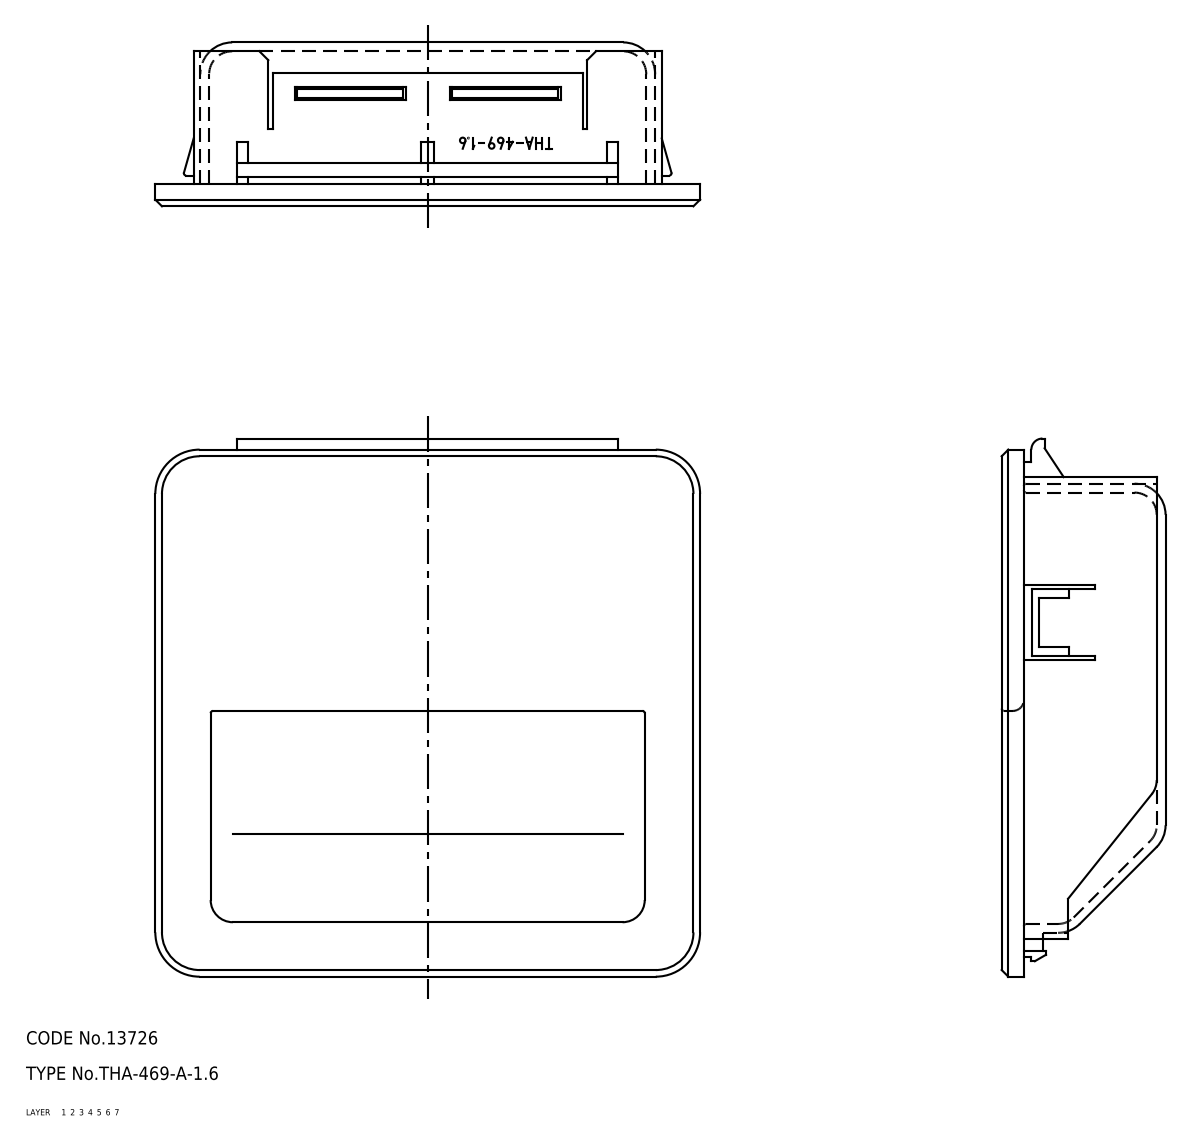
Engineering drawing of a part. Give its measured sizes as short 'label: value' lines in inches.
name: 0010; THA_469_A_1_6
written by: SolidWorks 2015 (AUTOMOTIVE_DESIGN)
unit: in
bodies: 1 solid, 754 faces (303 planar, 222 cylindrical, 229 other)
size: 4.843 × 4.783 × 1.457
volume: 5.884 in³; area: 110.6 in²
holes: 43× ⌀0.276
rounds: 59× R0.02, 12× R0.197, 11× R0.276, 8× R0.012, 4× R0.024, 4× R0.138, 4× R0.315, 4× R0.335
face distances: 0.079, 1.26, 1.378, 1.457, 0.138, 0.197, 1.181, 4.024, 0.118, 1.339
hole spacings: 0.446, 0.739, 1.115, 0.417, 1.513, 0.891, 0.835, 1.148
